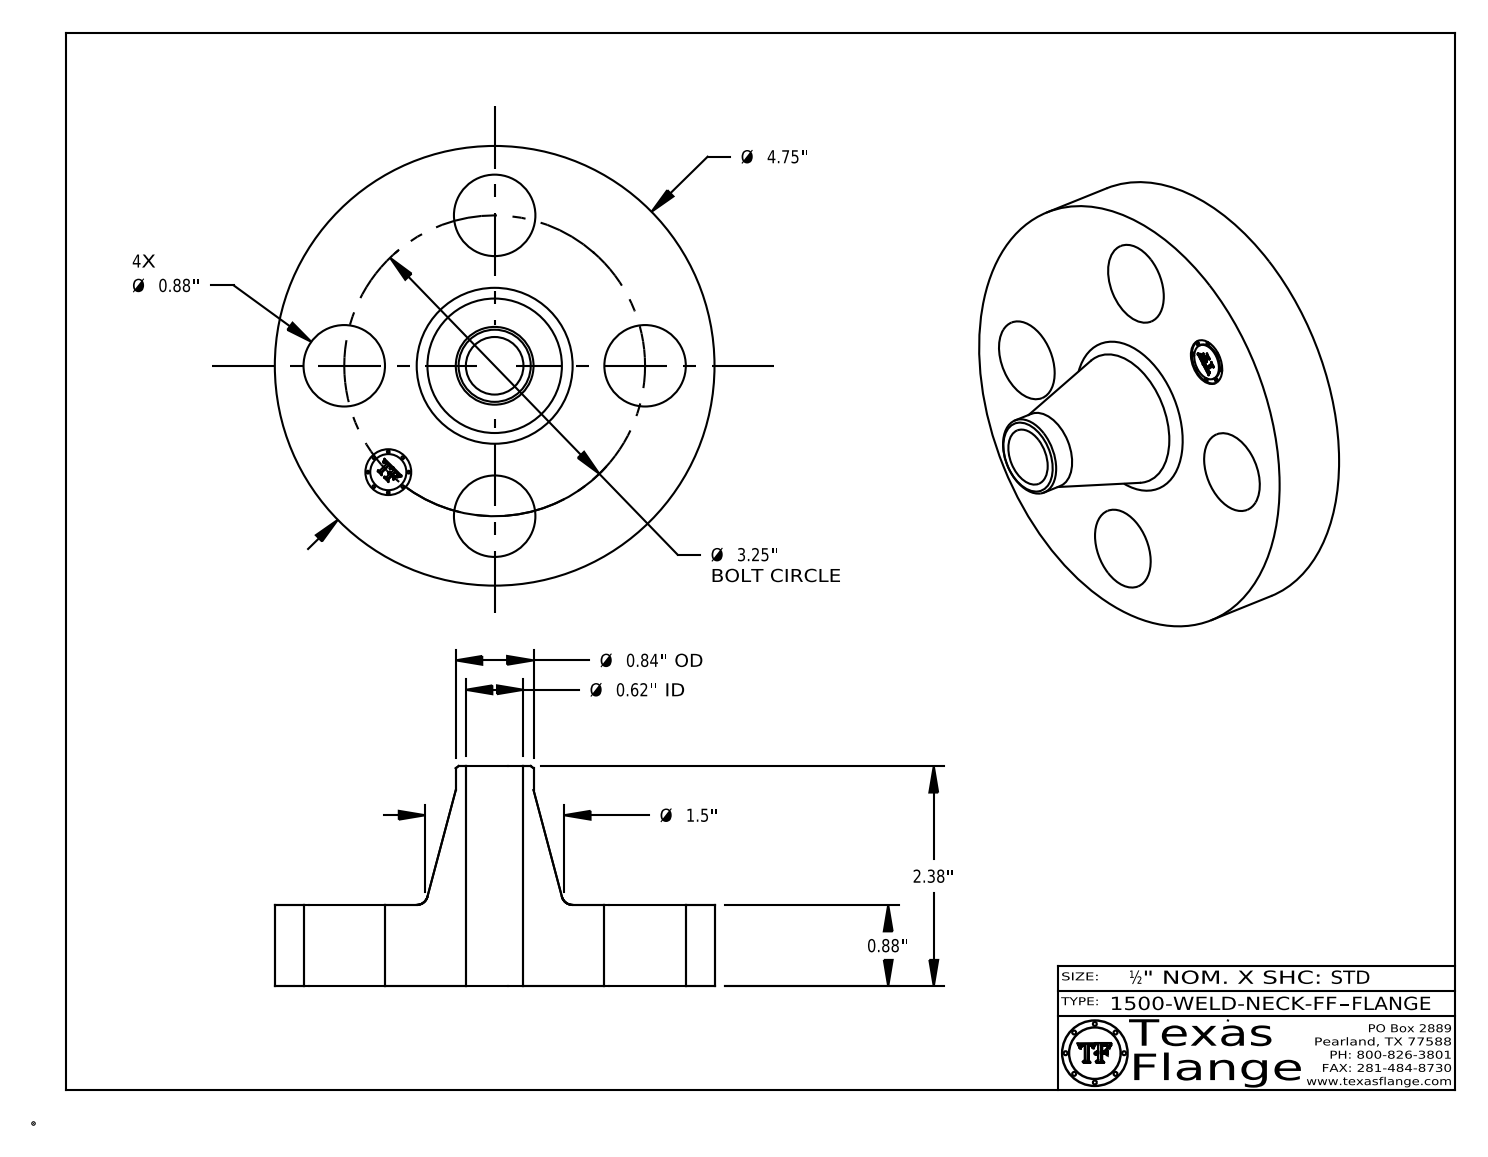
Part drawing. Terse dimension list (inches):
name: 1500-WELD-NECK-FF
written by: CATIA V5 STEP AP214 (AUTOMOTIVE_DESIGN)
unit: in
bodies: 1 solid, 408 faces (368 planar, 34 cylindrical, 6 other)
size: 4.75 × 4.75 × 2.38
volume: 14.25 in³; area: 61.6 in²
holes: 4× ⌀0.88, 1× ⌀0.495, 1× ⌀0.622
bosses: 8× ⌀0.03, 1× ⌀4.75, 1× ⌀0.84, 1× ⌀0.39
face distances: 0.88, 2.38, 1.5, 0.865, 0.015, 1.515, 0.148, 0.144, 0.027, 0.096
hole spacings: 1.625, 2.298, 1.244, 3.003, 3.25
